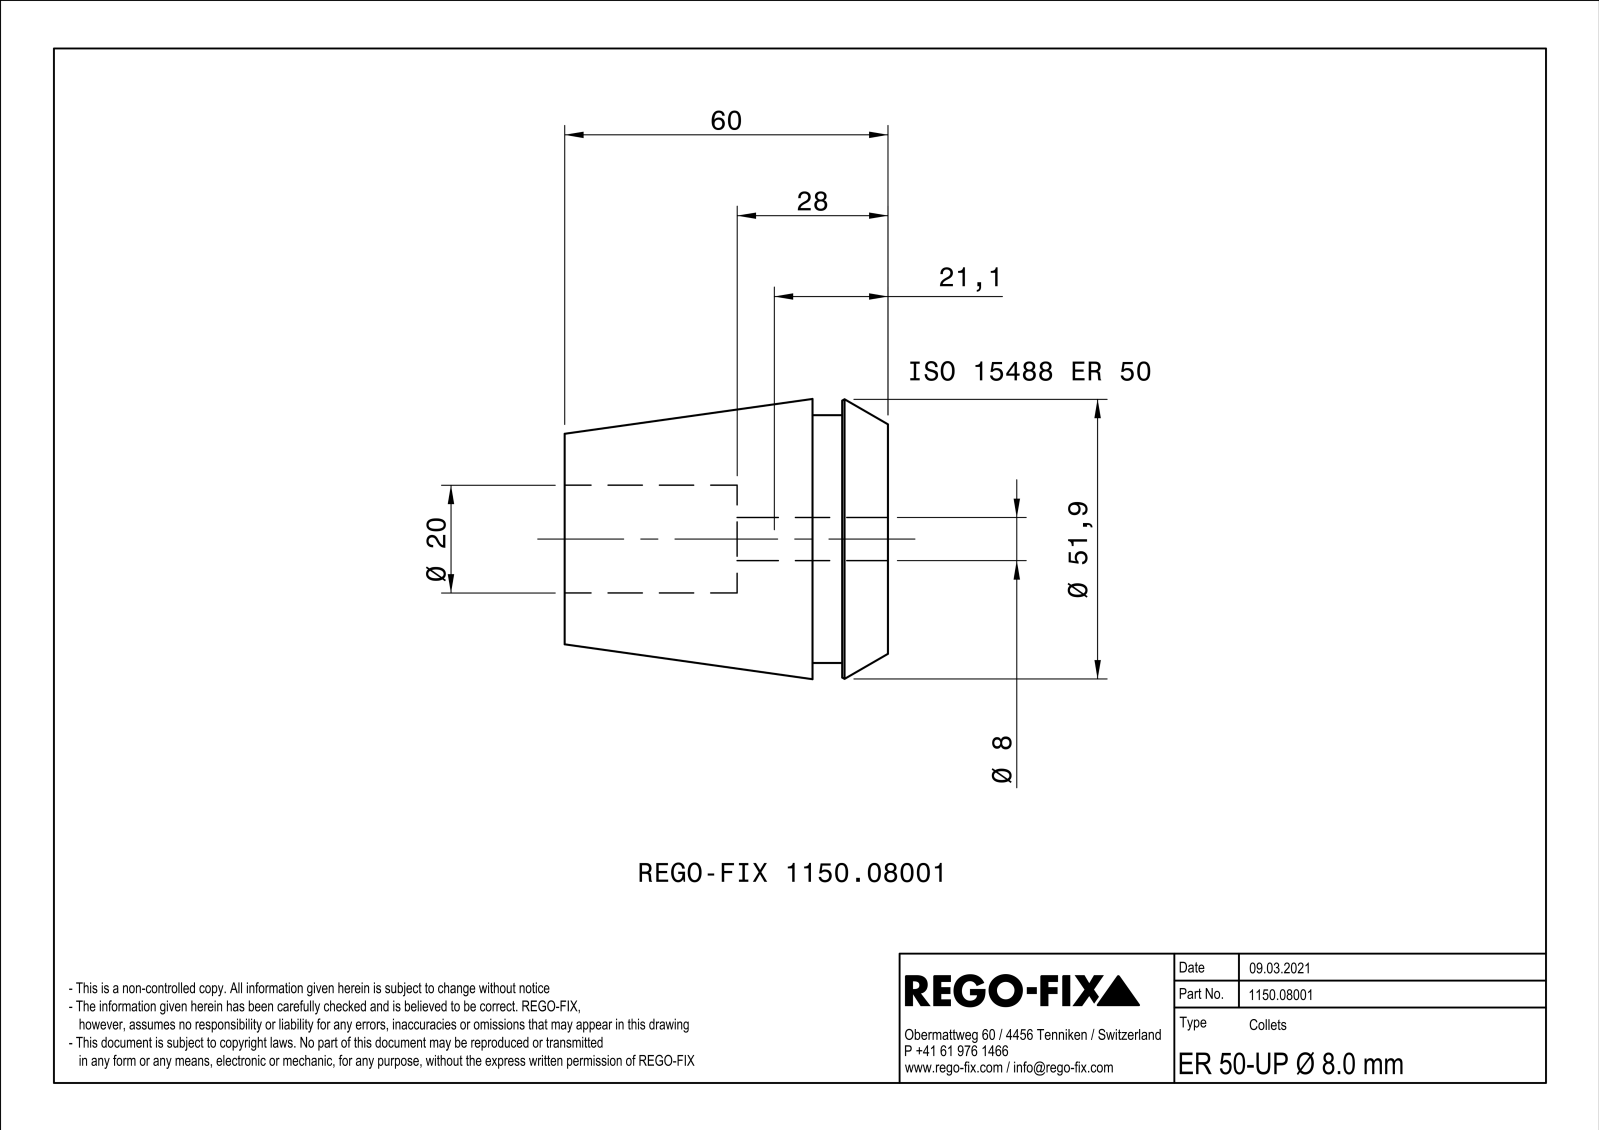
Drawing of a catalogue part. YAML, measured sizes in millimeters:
part_name: "NOCUT"
step_written_by: "SIEMENS PLM Software Solid Edge ST10 (AUTOMOTIVE_DESIGN)"
units: millimeters
bodies: {solids: 1, faces: 288, planar: 120, cylindrical: 32, other: 136}
overall_size: [60, 51.99, 51.99]
volume: 75764
surface_area: 38094
round_holes:
  - {diameter: 20, count: 1}
round_bosses_or_shafts:
  - {diameter: 46, count: 1}
partial_cylinders:
  - {radius: 4, count: 1}
face_to_face_distances: [1, 1.02, 0.98, 60, 14, 46, 8.5, 5.5, 51.5, 28]
